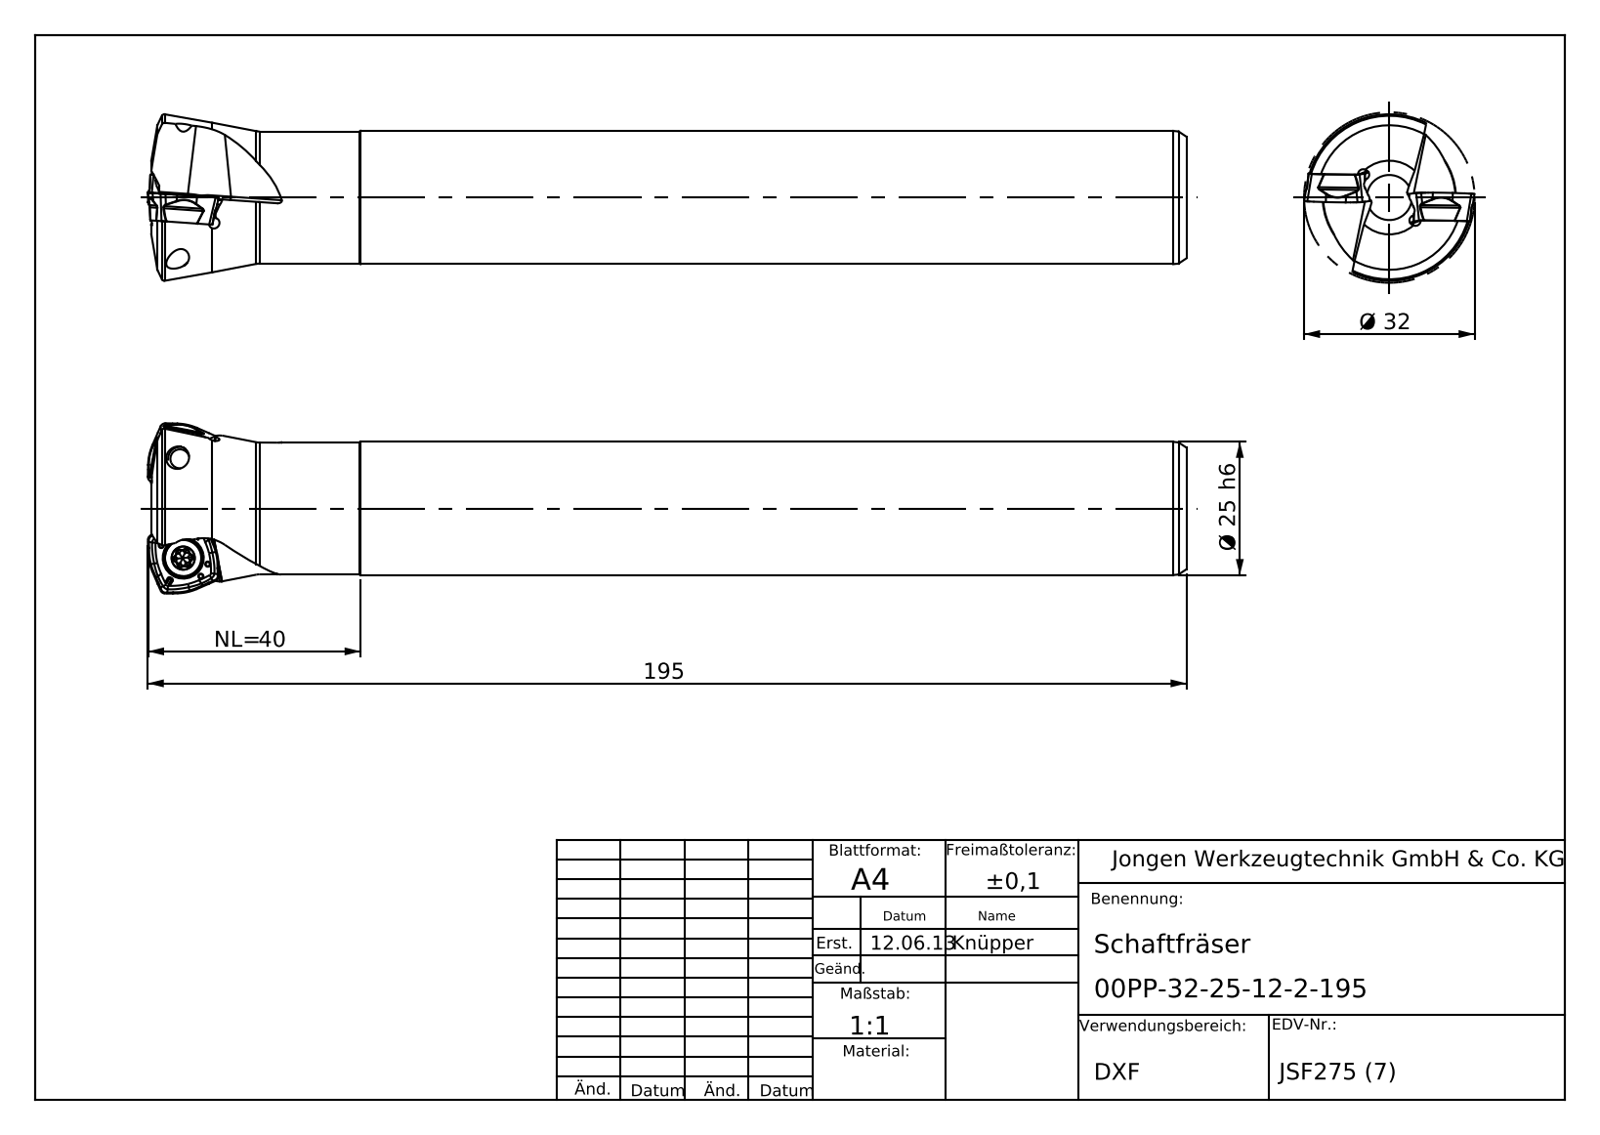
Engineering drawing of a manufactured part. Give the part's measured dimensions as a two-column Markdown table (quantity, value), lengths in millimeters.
| quantity | value |
| --- | --- |
| part name | 00PP-32-25-12-2-195 |
| STEP written by | SolidWorks 2013 (AUTOMOTIVE_DESIGN) |
| units | millimeters |
| bodies | 1 solid, 88 faces (36 planar, 20 cylindrical, 32 other) |
| overall size | 194.95 × 31.97 × 31.97 |
| volume | 97 356 mm³ |
| surface area | 17 086 mm² |
| round bosses / shafts (diameter × count) | 25 × 1, 24.8 × 1 |
| partial cylindrical surfaces (radius × count) | 0.5 × 4, 1.3 × 4, 1 × 2, 2 × 2 |
| main face-to-face distances | 192.75, 4.85 |
